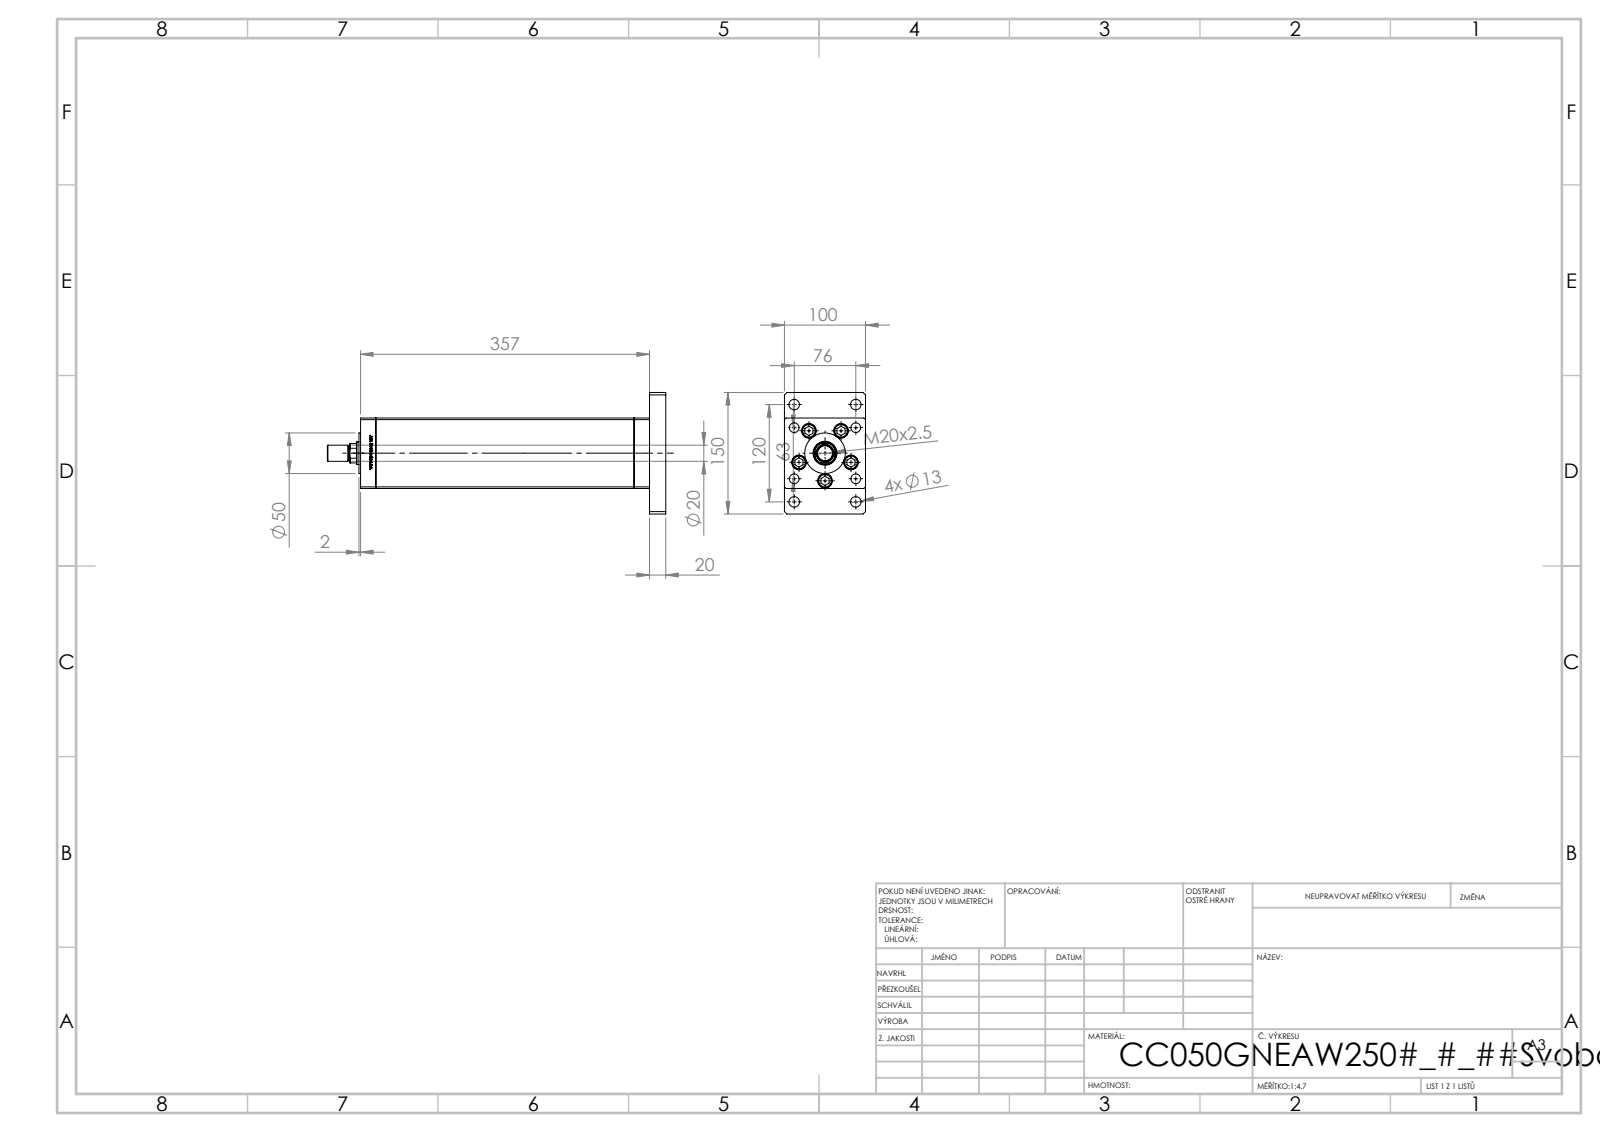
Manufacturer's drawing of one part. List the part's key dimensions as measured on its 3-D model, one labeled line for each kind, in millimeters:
Part name (STEP PRODUCT): V220C_F; V220CC_MALE_METRIC; V220C_FRONT_G; V220C_G_MIDDLE (+3 more)
STEP written by: SolidWorks 2019 (CONFIG_CONTROL_DESIGN)
Units: millimetres
Bodies: 20 solids, 1324 faces (521 planar, 191 cylindrical, 612 other)
Overall size (bounding box): 417.5 × 150 × 100
Volume: 2 922 000 mm³ · Surface area: 367 705 mm²
Round holes (diameter × count): ⌀12 ×9, ⌀13.5 ×5, ⌀18 ×5, ⌀13 ×4, ⌀17 ×4, ⌀2 ×2, ⌀13.16 ×2, ⌀18.5 ×1, ⌀28 ×1, ⌀29.5 ×1, ⌀68 ×1
Round bosses / shafts (diameter × count): ⌀8 ×9, ⌀17 ×5, ⌀50 ×1, ⌀20 ×1, ⌀18 ×1
Partial cylindrical surfaces — rounded edges, fillets, slot ends (radius × count): R0.93 ×2, R13.5 ×1
Main face-to-face distances: 100, 87, 19, 337.5, 318.5, 20, 357.5, 39, 376.5, 356.5
Hole centre spacings: 34, 28.5, 49.36, 71.02, 76, 81.17, 91.5, 118.95
